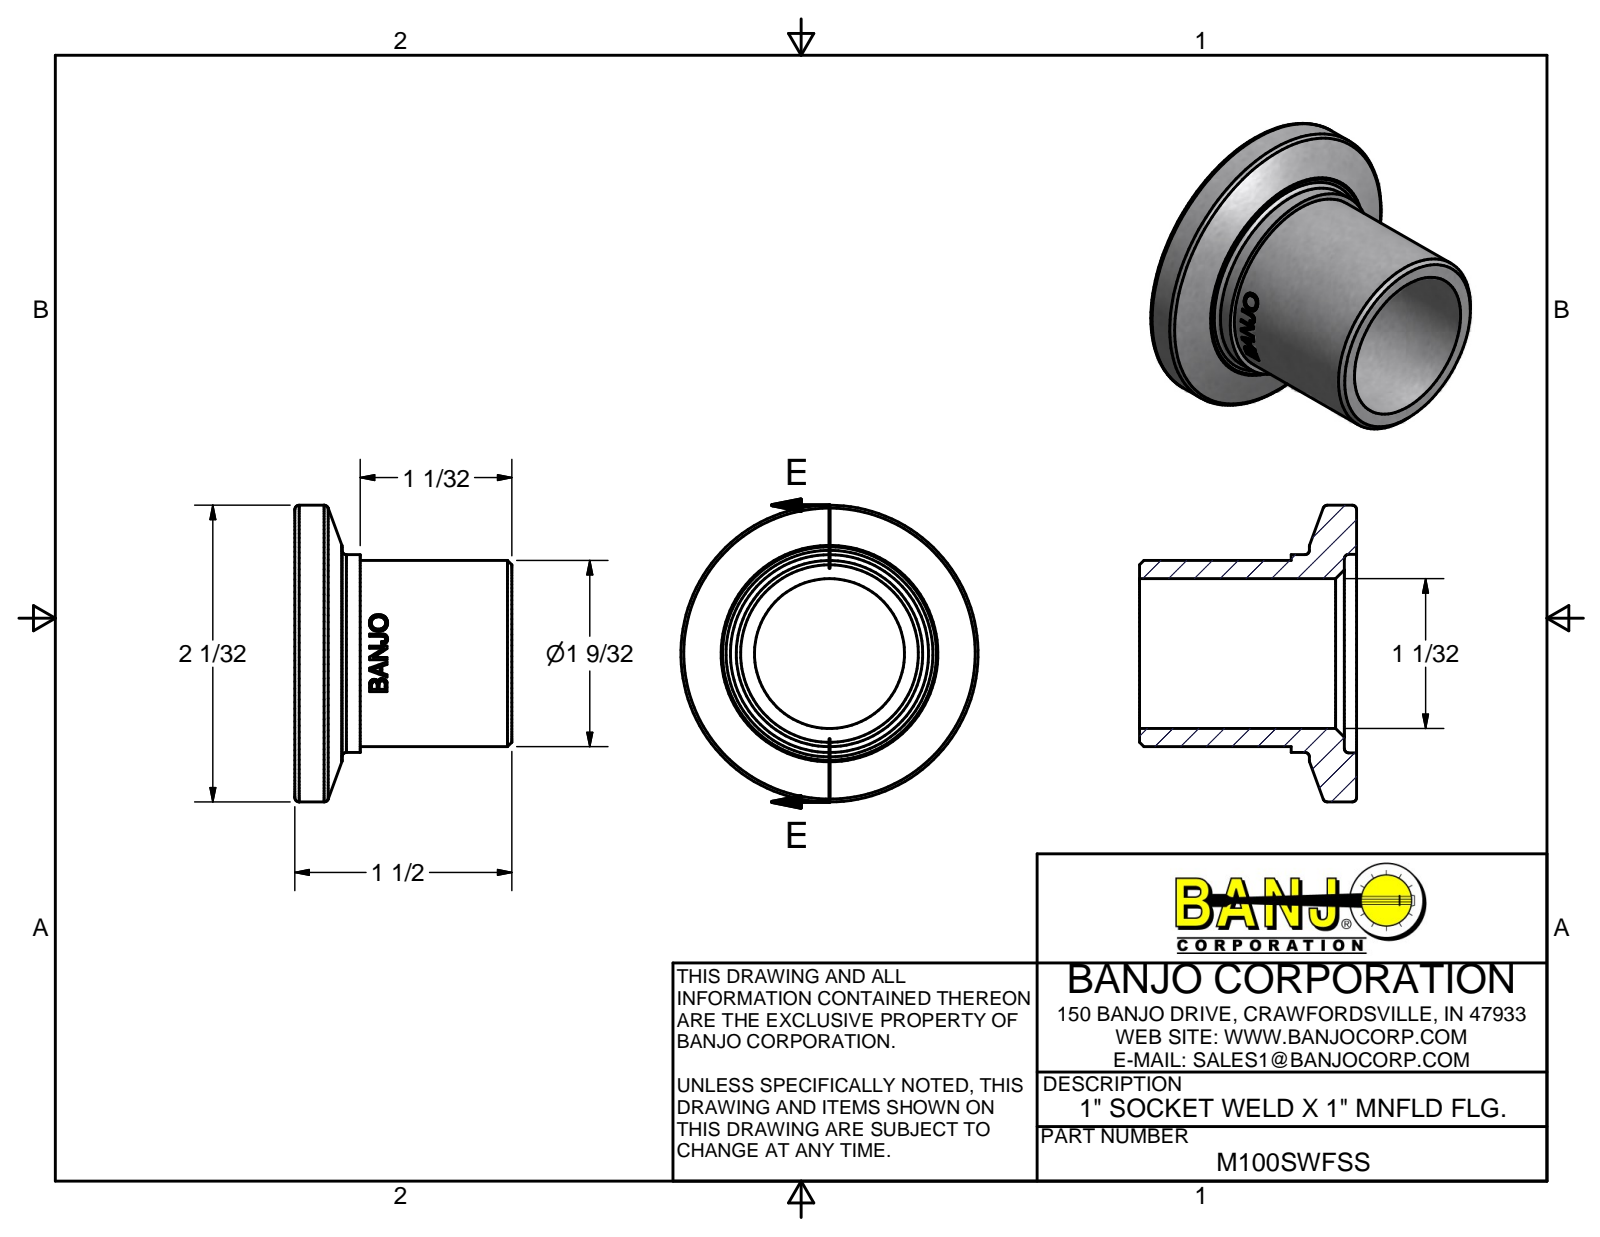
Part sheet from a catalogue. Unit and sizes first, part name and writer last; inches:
Units: inches
Overall size (bounding box): 2.04 × 2.04 × 1.49
Round holes (diameter × count): ⌀1.03 ×1, ⌀1.365 ×1
Round bosses / shafts (diameter × count): ⌀2.04 ×1, ⌀1.36 ×1, ⌀1.28 ×1
Partial cylindrical surfaces — rounded edges, fillets, slot ends (radius × count): R0.61 ×1
Main face-to-face distances: 1.49, 1.406, 0.084, 1.041, 0.365, 0.449, 0.241, 1.166, 0.125, 0.324
Volume: 1.193 in³ · Surface area: 15.9 in²
Bodies: 1 solid, 235 faces (99 planar, 25 cylindrical, 111 other)
Part name (STEP PRODUCT): M100SWFSS
STEP written by: Autodesk Inventor 2014 (AUTOMOTIVE_DESIGN)
